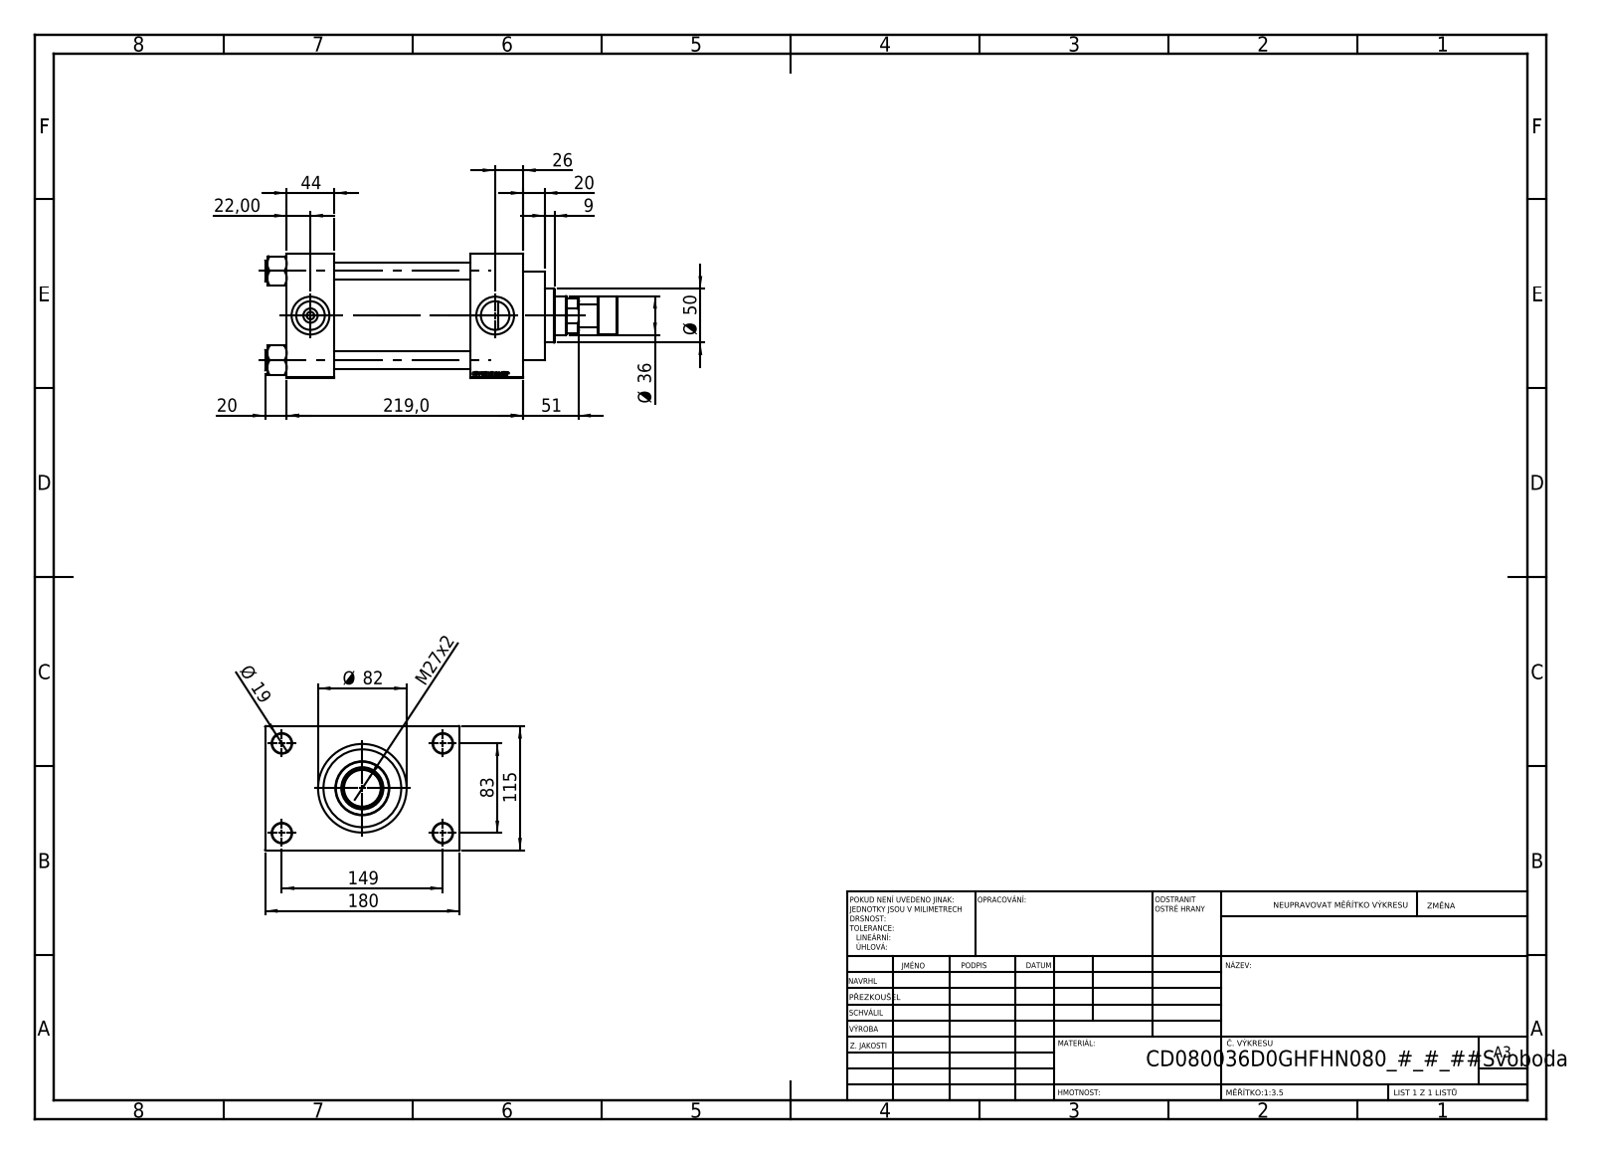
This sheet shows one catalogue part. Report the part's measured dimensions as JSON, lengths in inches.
{"part_name": "V215CD_D_Body; V215CD_NUT_M5_D; V215CD_VCP_D; V215CR_ROD_END_F (+2 more)", "step_written_by": "SolidWorks 2019 (CONFIG_CONTROL_DESIGN)", "units": "inches", "bodies": {"solids": 12, "faces": 1165, "planar": 549, "cylindrical": 92, "other": 524}, "overall_size": [12.835, 7.087, 4.528], "volume_in3": 131.8, "surface_area_in2": 546.1, "round_holes": [[0.63, 4], [0.709, 4], [0.276, 2], [1.041, 2], [1.378, 2], [1.004, 1], [1.417, 1], [1.535, 1], [2.402, 1], [2.835, 1], [3.15, 1]], "round_bosses_or_shafts": [[0.748, 4], [3.386, 1], [3.228, 1], [1.969, 1], [1.378, 1], [0.827, 1]], "face_to_face_distances": [4.528, 4.961, 1.929, 6.89, 6.693, 1.732, 8.622, 1.28, 5.807, 7.087], "hole_center_spacings": [1.305, 2.302, 3.256, 3.357, 3.513, 4.561, 5.607, 3.268]}
